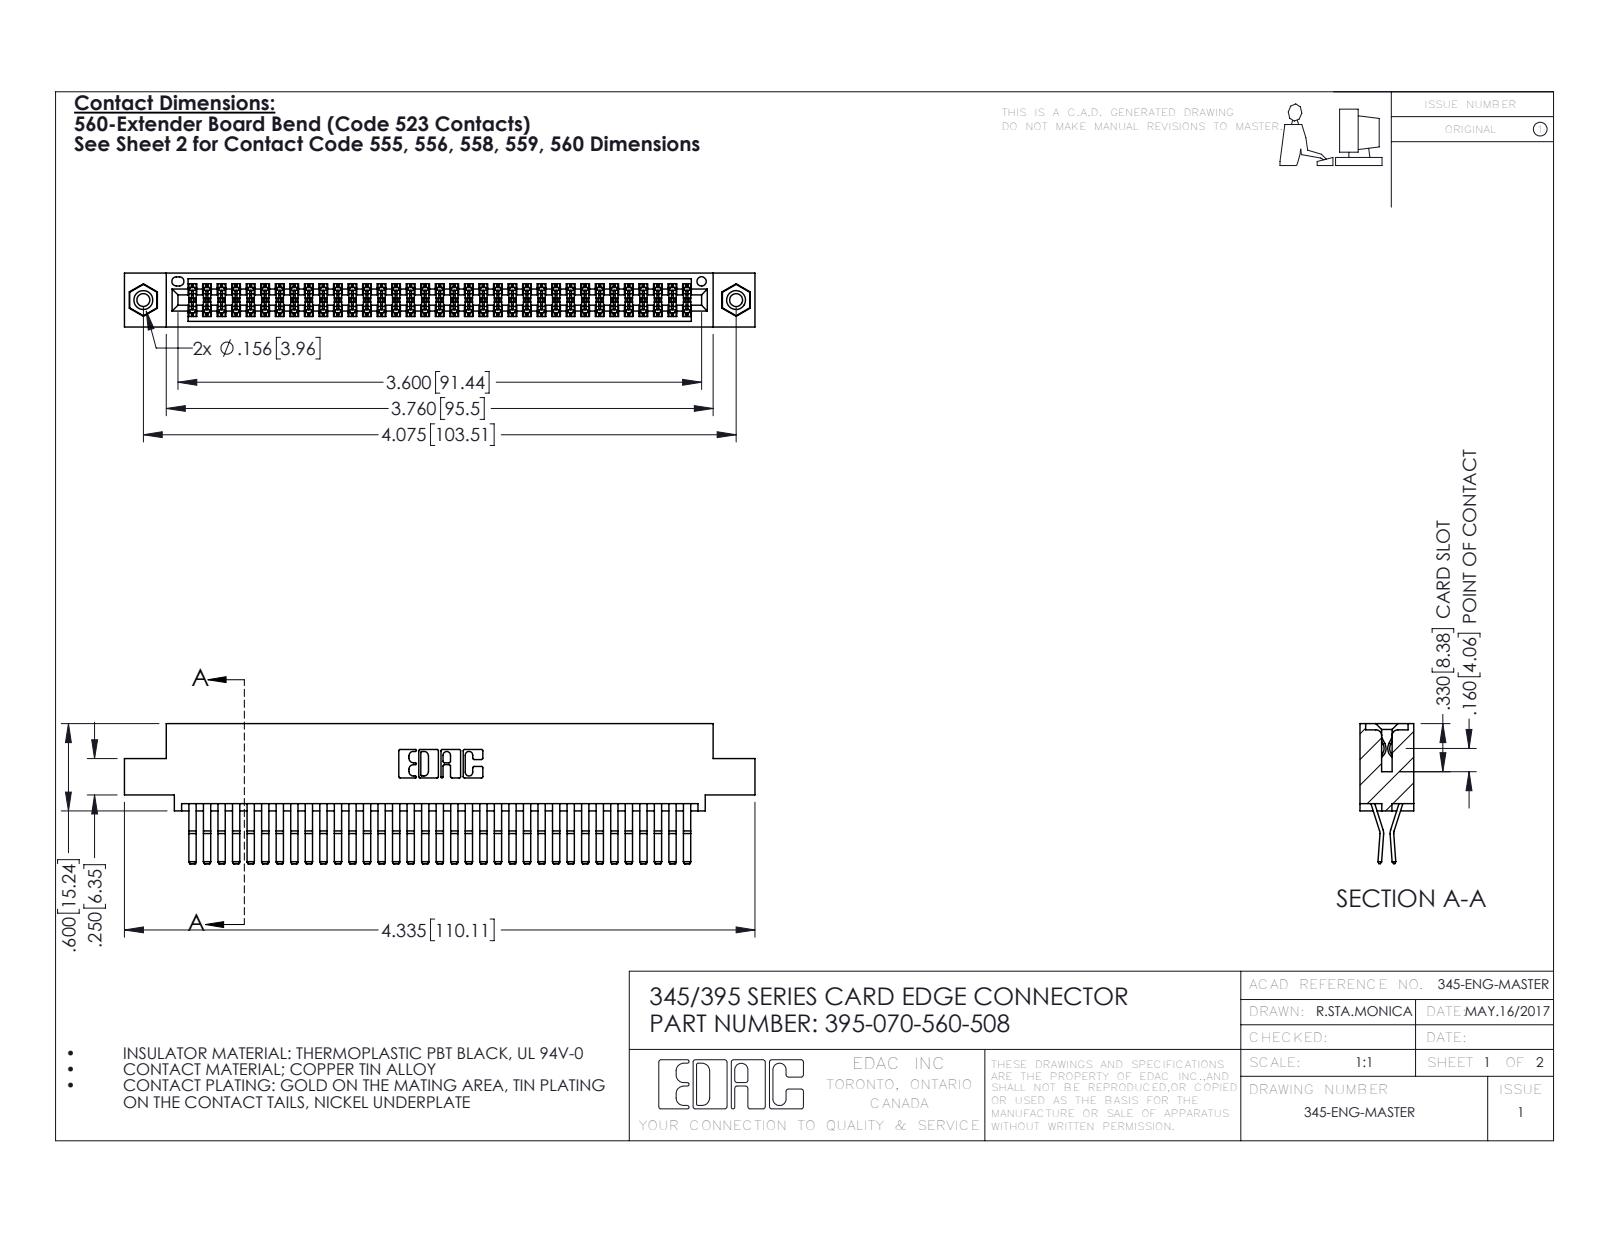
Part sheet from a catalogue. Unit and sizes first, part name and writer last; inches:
Units: inches
Overall size (bounding box): 4.335 × 0.962 × 0.37
Round holes (diameter × count): ⌀0.089 ×2, ⌀0.125 ×2, ⌀0.156 ×2, ⌀0.064 ×1
Round bosses / shafts (diameter × count): ⌀0.155 ×2
Partial cylindrical surfaces — rounded edges, fillets, slot ends (radius × count): R0.006 ×105, R0.01 ×22, R0.007 ×6, R0.031 ×6, R0.026 ×3, R0.01 ×2, R0.014 ×2, R0.019 ×2
Main face-to-face distances: 0.025, 0.072, 0.298, 0.37, 0.2, 0.098, 0.272, 0.225, 0.175, 0.149
Hole centre spacings: 0.27, 3.839, 4.075
Volume: 0.672 in³ · Surface area: 27.01 in²
Bodies: 73 solids, 3830 faces (2426 planar, 1388 cylindrical, 16 other)
Part name (STEP PRODUCT): 395-070-560-508; 345-292-001_560 Tail; 345 Part_0.110 Offset - 0.156 Dia-TI; 345-250-001_345-250-003-102
STEP written by: SolidWorks 2016 (CONFIG_CONTROL_DESIGN)
